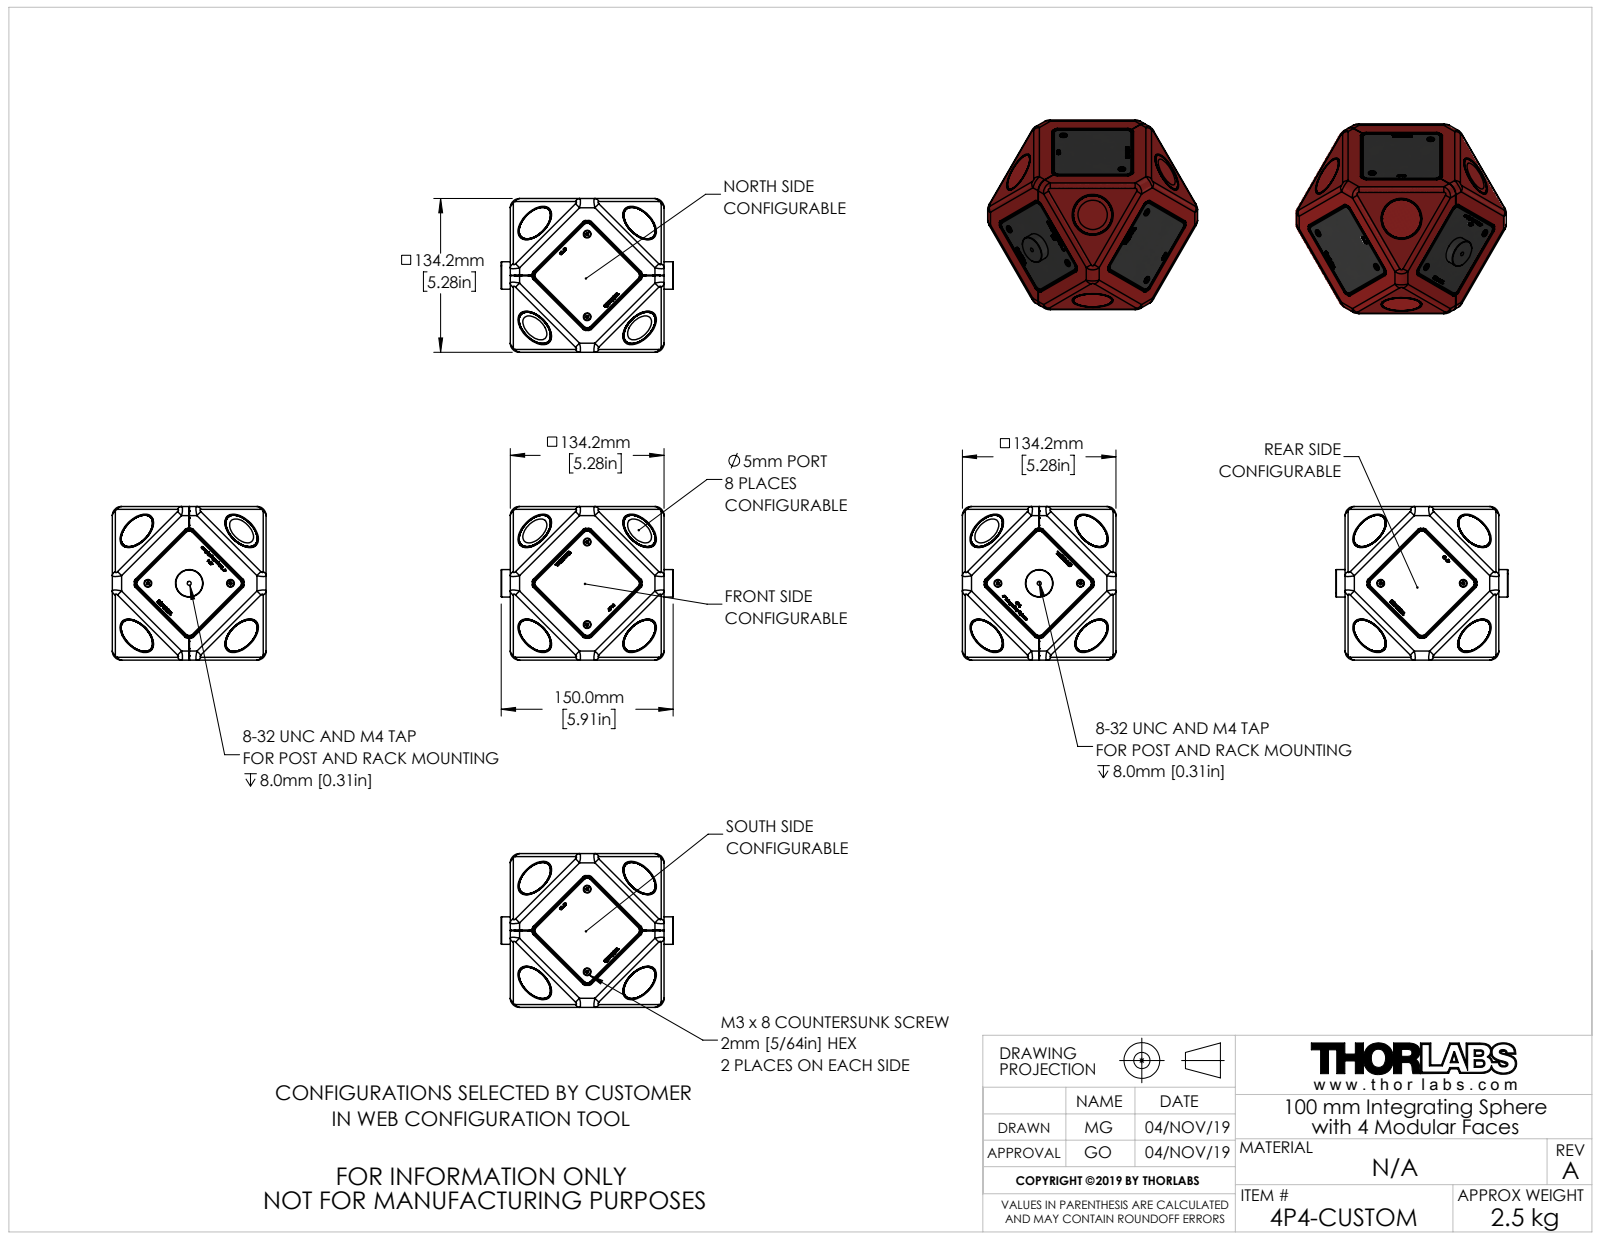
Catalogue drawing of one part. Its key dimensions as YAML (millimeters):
part_name: "19.11.08_4P4-CUSTOM"
step_written_by: "SolidWorks 2018 (AUTOMOTIVE_DESIGN)"
units: millimeters
bodies: {solids: 0, faces: 6728, planar: 4306, cylindrical: 1086, other: 1336}
overall_size: [150, 134.2, 134.2]
round_holes:
  - {diameter: 5.5, count: 13}
  - {diameter: 4, count: 11}
  - {diameter: 4.5, count: 11}
  - {diameter: 6.5, count: 11}
  - {diameter: 2.5, count: 8}
  - {diameter: 3.2, count: 8}
  - {diameter: 30.5, count: 8}
  - {diameter: 32.3, count: 8}
  - {diameter: 34.8, count: 8}
  - {diameter: 25.6, count: 2}
  - {diameter: 27, count: 2}
  - {diameter: 3.45, count: 1}
round_bosses_or_shafts:
  - {diameter: 34.1, count: 8}
  - {diameter: 34, count: 8}
  - {diameter: 32, count: 8}
  - {diameter: 5.7, count: 8}
  - {diameter: 3, count: 8}
  - {diameter: 5.5, count: 3}
  - {diameter: 24, count: 1}
partial_cylinders:
  - {radius: 1, count: 188}
  - {radius: 0.25, count: 64}
  - {radius: 0.5, count: 56}
  - {radius: 2, count: 56}
  - {radius: 6, count: 36}
  - {radius: 0.2, count: 32}
  - {radius: 0.8, count: 32}
  - {radius: 2.5, count: 24}
face_to_face_distances: [3, 131, 128, 3.1, 131.1, 134.1, 4.9, 126.1, 118.2, 7.99]
hole_center_spacings: [16.84, 25.74, 40.66, 53.91, 31.12, 42.24, 14.06, 36.06]
